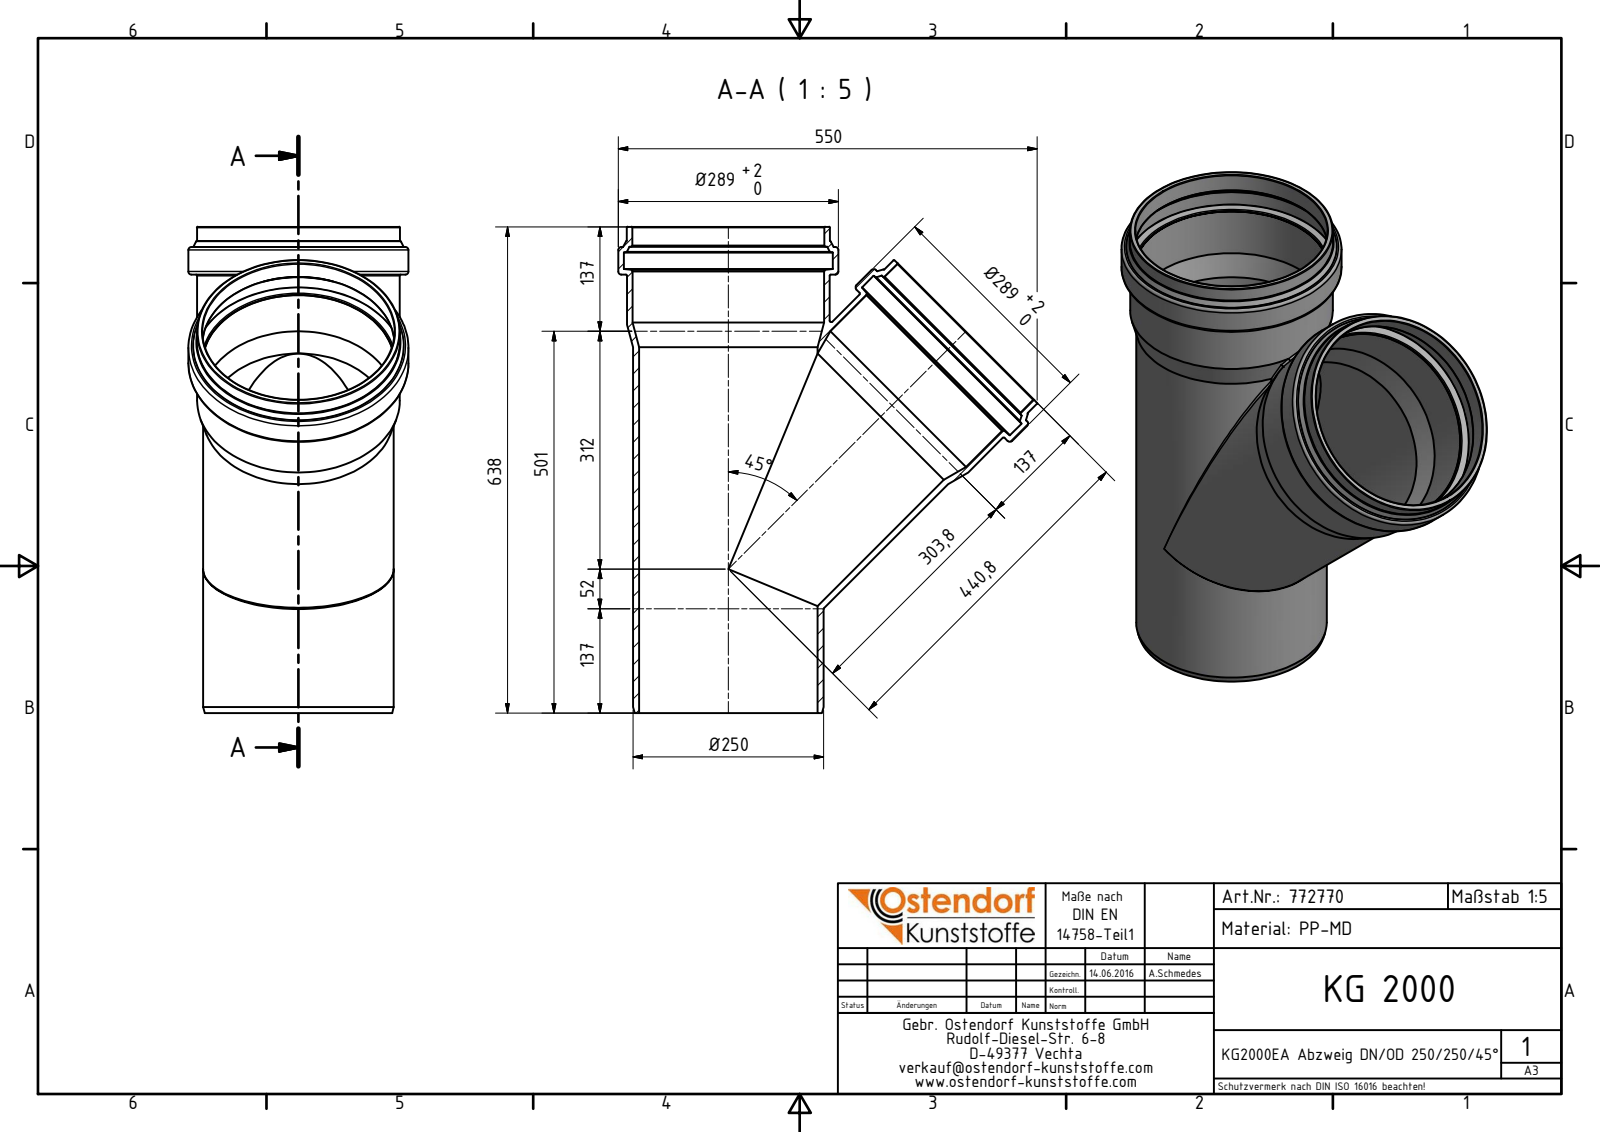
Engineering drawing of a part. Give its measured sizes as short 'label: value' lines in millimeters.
name: 772770 KG2000EA Abzweig DN_OD 250_250_45°
written by: Autodesk Inventor 2016 (AUTOMOTIVE_DESIGN)
unit: mm
bodies: 1 solid, 78 faces (9 planar, 18 cylindrical, 51 other)
size: 638 × 550 × 289
volume: 5 431 000 mm³; area: 1 417 000 mm²
holes: 3× ⌀252.1, 2× ⌀234.3, 2× ⌀251.7, 2× ⌀274.6
bosses: 2× ⌀289, 2× ⌀266.5, 2× ⌀266.1, 2× ⌀250.3
face distances: 575.4, 62.59, 638, 62.6, 26.3, 36.29, 611.7, 36.3, 32.08, 58.38
